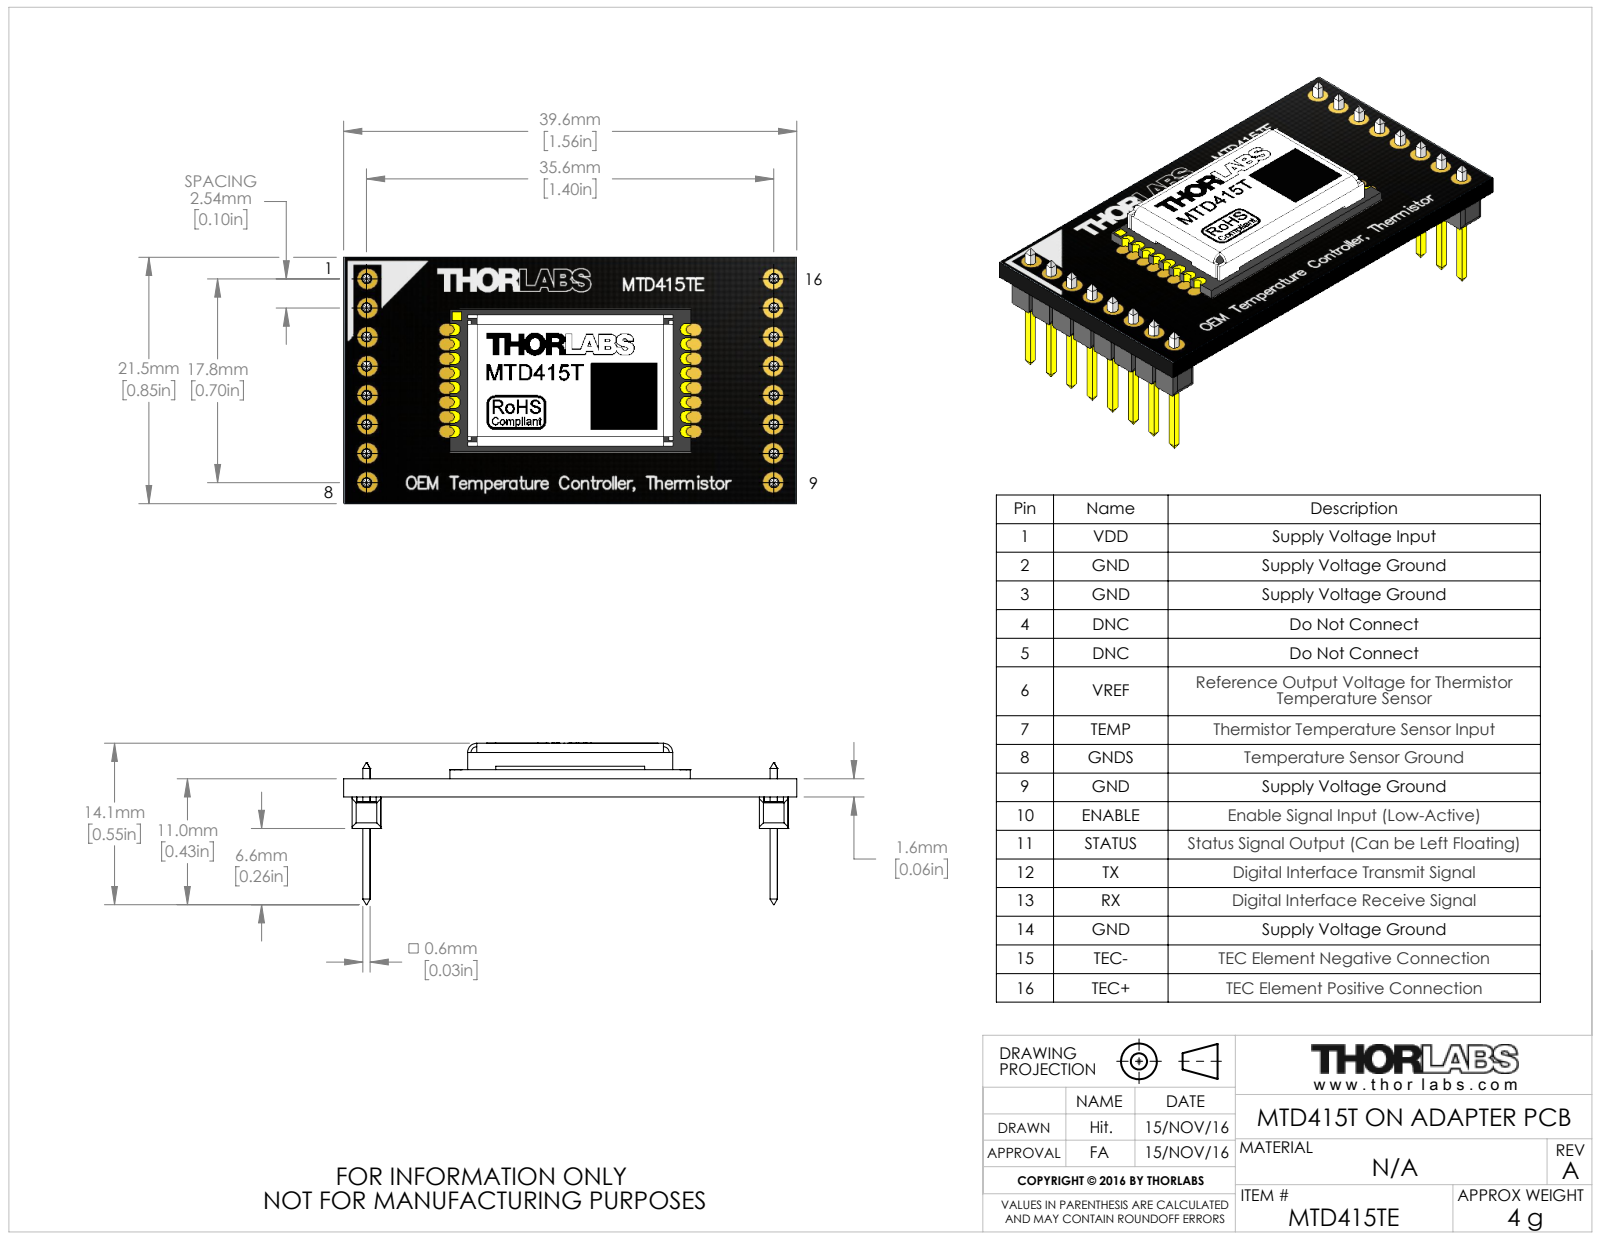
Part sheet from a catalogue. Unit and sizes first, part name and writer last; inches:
Units: inches
Overall size (bounding box): 1.557 × 0.846 × 0.555
Round holes (diameter × count): ⌀0.035 ×16
Partial cylindrical surfaces — rounded edges, fillets, slot ends (radius × count): R0.015 ×16, R0.021 ×16, R0.02 ×4, R0.022 ×4, R0.03 ×4, R0.031 ×4
Main face-to-face distances: 0.063, 0.031, 0.094, 1.4, 0.037, 0.062, 0.079, 0.122, 0.091, 0.173
Hole centre spacings: 0.1, 1.404, 0.2, 1.414, 0.3, 1.432, 0.4, 1.4
Volume: 0.118 in³ · Surface area: 6.353 in²
Bodies: 19 solids, 1554 faces (1315 planar, 120 cylindrical, 119 other)
Part name (STEP PRODUCT): MTN007873-E0W
STEP written by: SolidWorks 2016 (AUTOMOTIVE_DESIGN)
